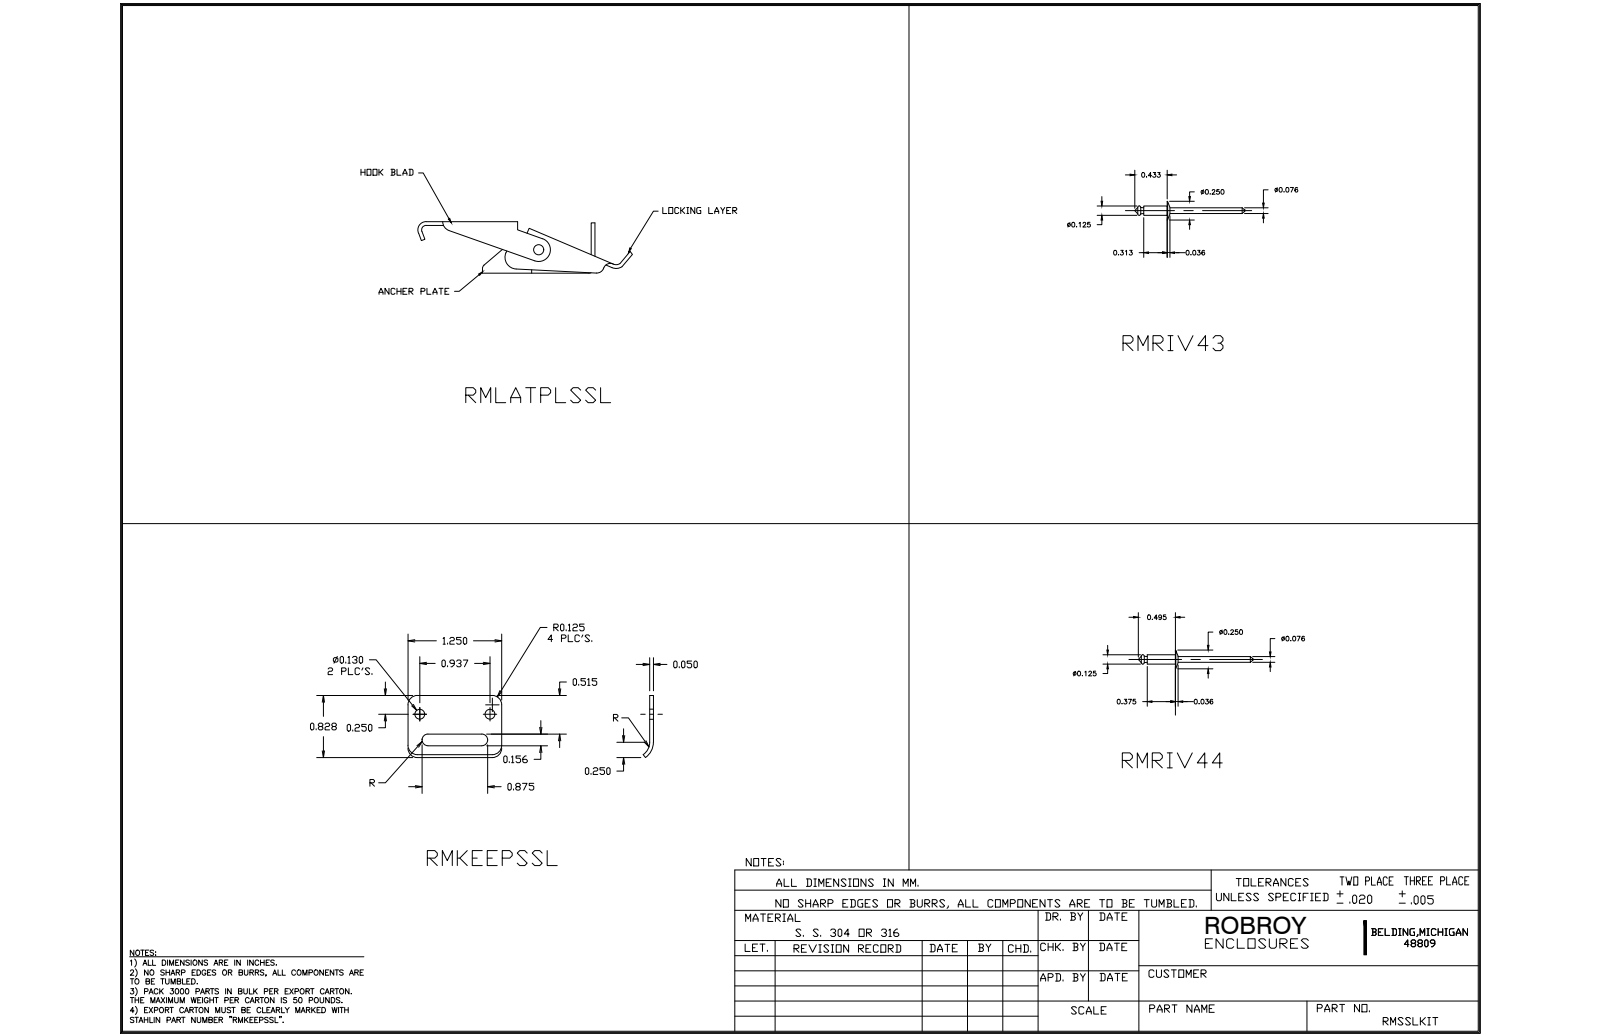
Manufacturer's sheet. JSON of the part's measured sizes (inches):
{"part_name": "SSLKIT", "step_written_by": "SolidWorks 2018 (AUTOMOTIVE_DESIGN)", "units": "inches", "bodies": {"solids": 10, "faces": 202, "planar": 91, "cylindrical": 91, "other": 20}, "overall_size": [3.614, 1.25, 0.813], "volume_in3": 0.381, "surface_area_in2": 17.47, "round_holes": [[0.104, 4], [0.13, 2], [0.135, 2], [0.14, 2], [0.135, 1], [0.375, 1]], "round_bosses_or_shafts": [[0.14, 2], [0.3, 1], [0.17, 1], [0.125, 1], [0.125, 1], [0.12, 1]], "partial_cylinders_radius": [[0.015, 12], [0.045, 8], [0.03, 6], [0.022, 5], [0.06, 4], [0.125, 4], [0.156, 4], [0.078, 2]], "face_to_face_distances": [0.05, 0.1, 0.94, 0.07, 0.999, 0.059, 0.051, 0.991, 0.87, 1.05], "hole_center_spacings": [0.937, 0.25, 0.75]}
